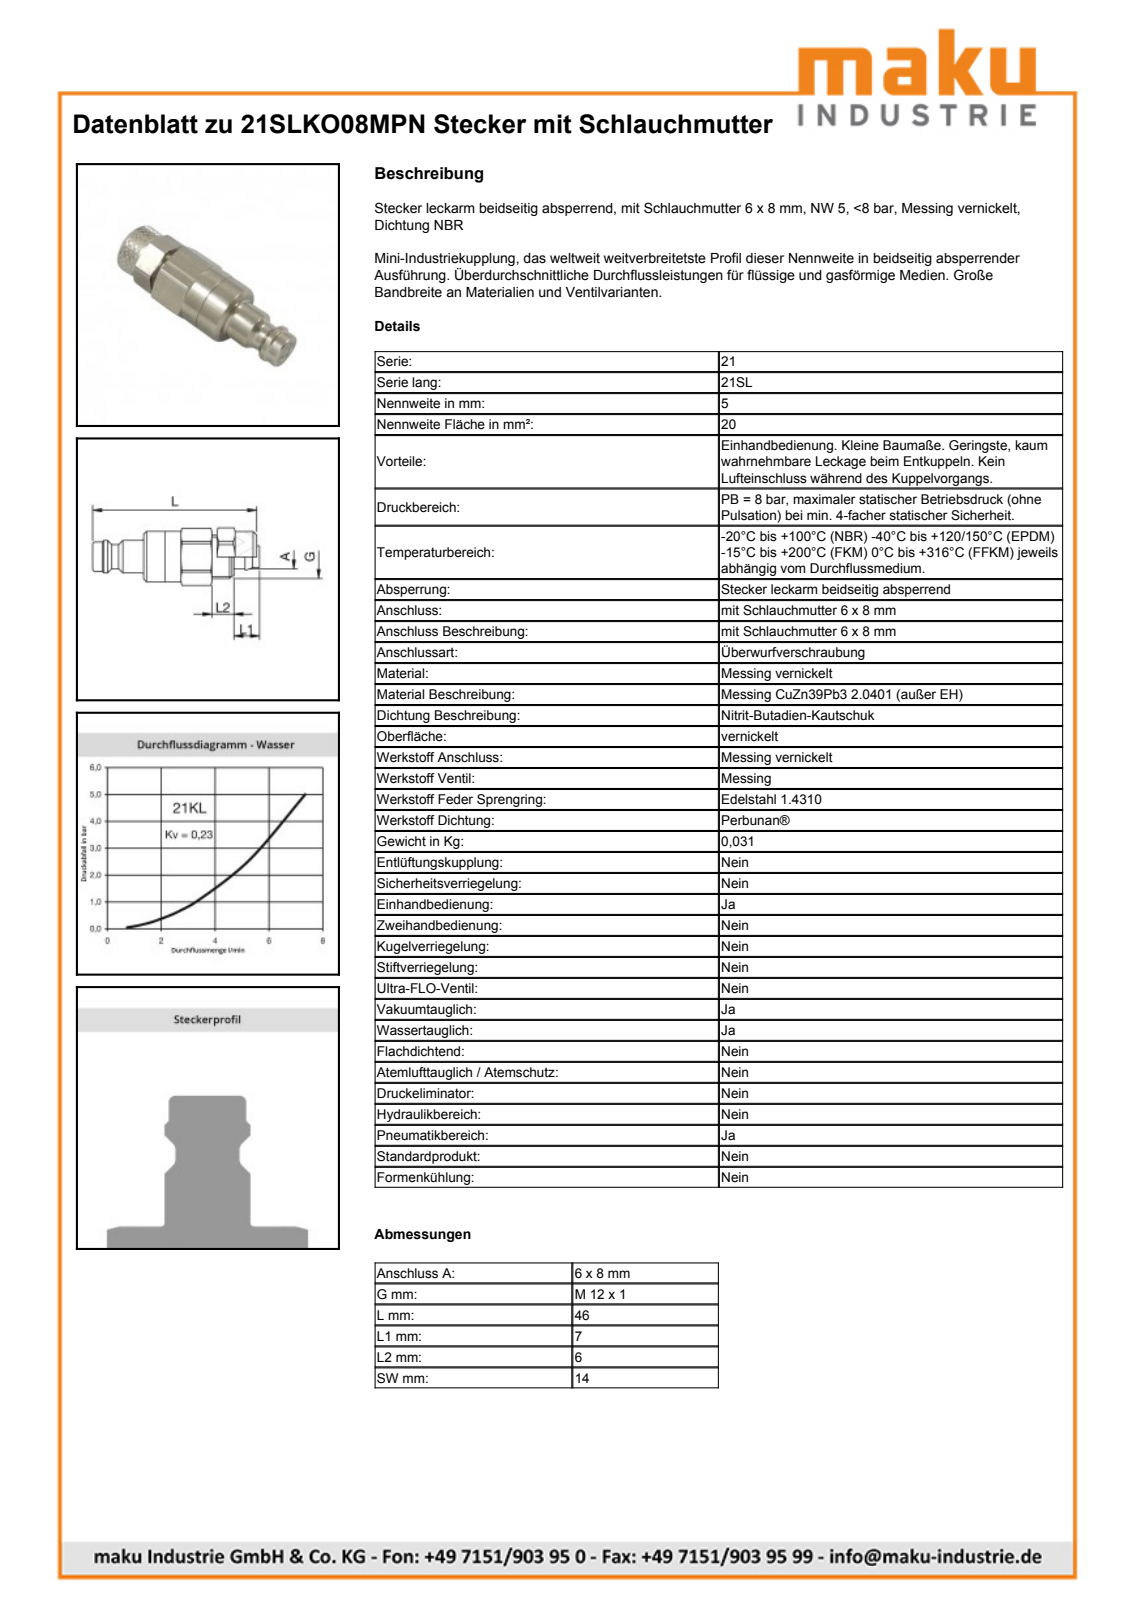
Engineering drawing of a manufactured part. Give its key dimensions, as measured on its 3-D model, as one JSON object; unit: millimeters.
{"part_name": "D113147", "step_written_by": "Autodesk Inventor 2013 (AUTOMOTIVE_DESIGN)", "units": "millimeters", "bodies": {"solids": 1, "faces": 106, "planar": 22, "cylindrical": 33, "other": 51}, "overall_size": [45.95, 15.72, 14.88], "volume_mm3": 4348, "surface_area_mm2": 4162, "round_holes": [[5.5, 1], [7.2, 1], [8.25, 1], [9.5, 1], [10.45, 1], [11.15, 1], [12, 1]], "round_bosses_or_shafts": [[14, 1], [11.98, 1], [11, 1], [10.6, 1], [9, 1], [8.1, 1], [6.7, 1], [6.65, 1]], "partial_cylinders_radius": [[7.75, 1], [7.9, 1]], "face_to_face_distances": [14, 7.85, 12.75, 4.9, 16.9, 24.75, 29.65, 14.1, 31, 38.85]}
